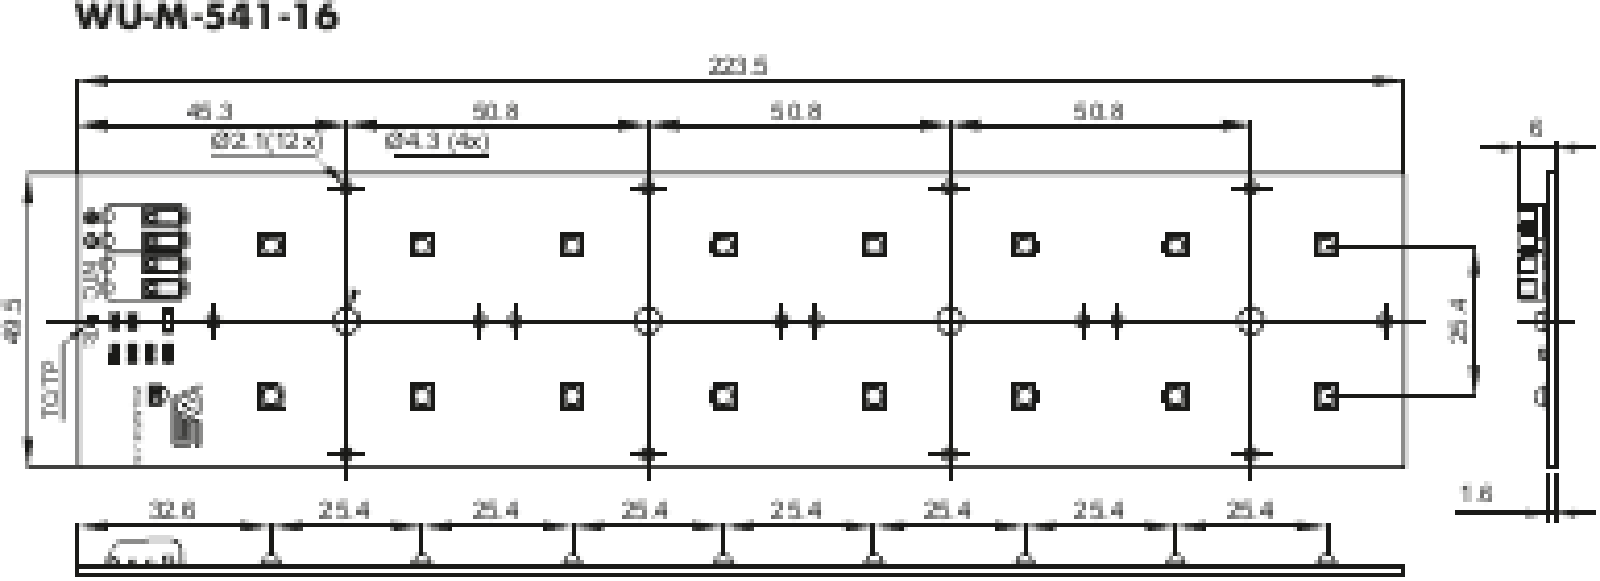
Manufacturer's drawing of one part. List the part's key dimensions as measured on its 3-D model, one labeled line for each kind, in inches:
Part name (STEP PRODUCT): SubSMA; PCB-Base WU-M-541-16; 2060-452; R0603 (+3 more)
STEP written by: SolidWorks 2016 (AUTOMOTIVE_DESIGN)
Units: inches
Bodies: 26 solids, 3391 faces (2349 planar, 560 cylindrical, 482 other)
Overall size (bounding box): 8.799 × 1.949 × 0.24
Volume: 1.117 in³ · Surface area: 38.51 in²
Round holes (diameter × count): ⌀0.083 ×16, ⌀0.089 ×4, ⌀0.169 ×4, ⌀0.07 ×2
Round bosses / shafts (diameter × count): ⌀0.09 ×2, ⌀0.059 ×1
Partial cylindrical surfaces — rounded edges, fillets, slot ends (radius × count): R0.008 ×205, R0.009 ×32, R0.051 ×32, R0.004 ×9, R0.087 ×8, R0.006 ×6, R0.009 ×3, R0.02 ×3
Main face-to-face distances: 0.063, 1.949, 0.069, 0.018, 0.315, 0.081, 0.138, 0.311, 0.14, 0.016
Hole centre spacings: 0.886, 1.253, 2, 1.423, 2.187, 3.019, 4, 1.772
